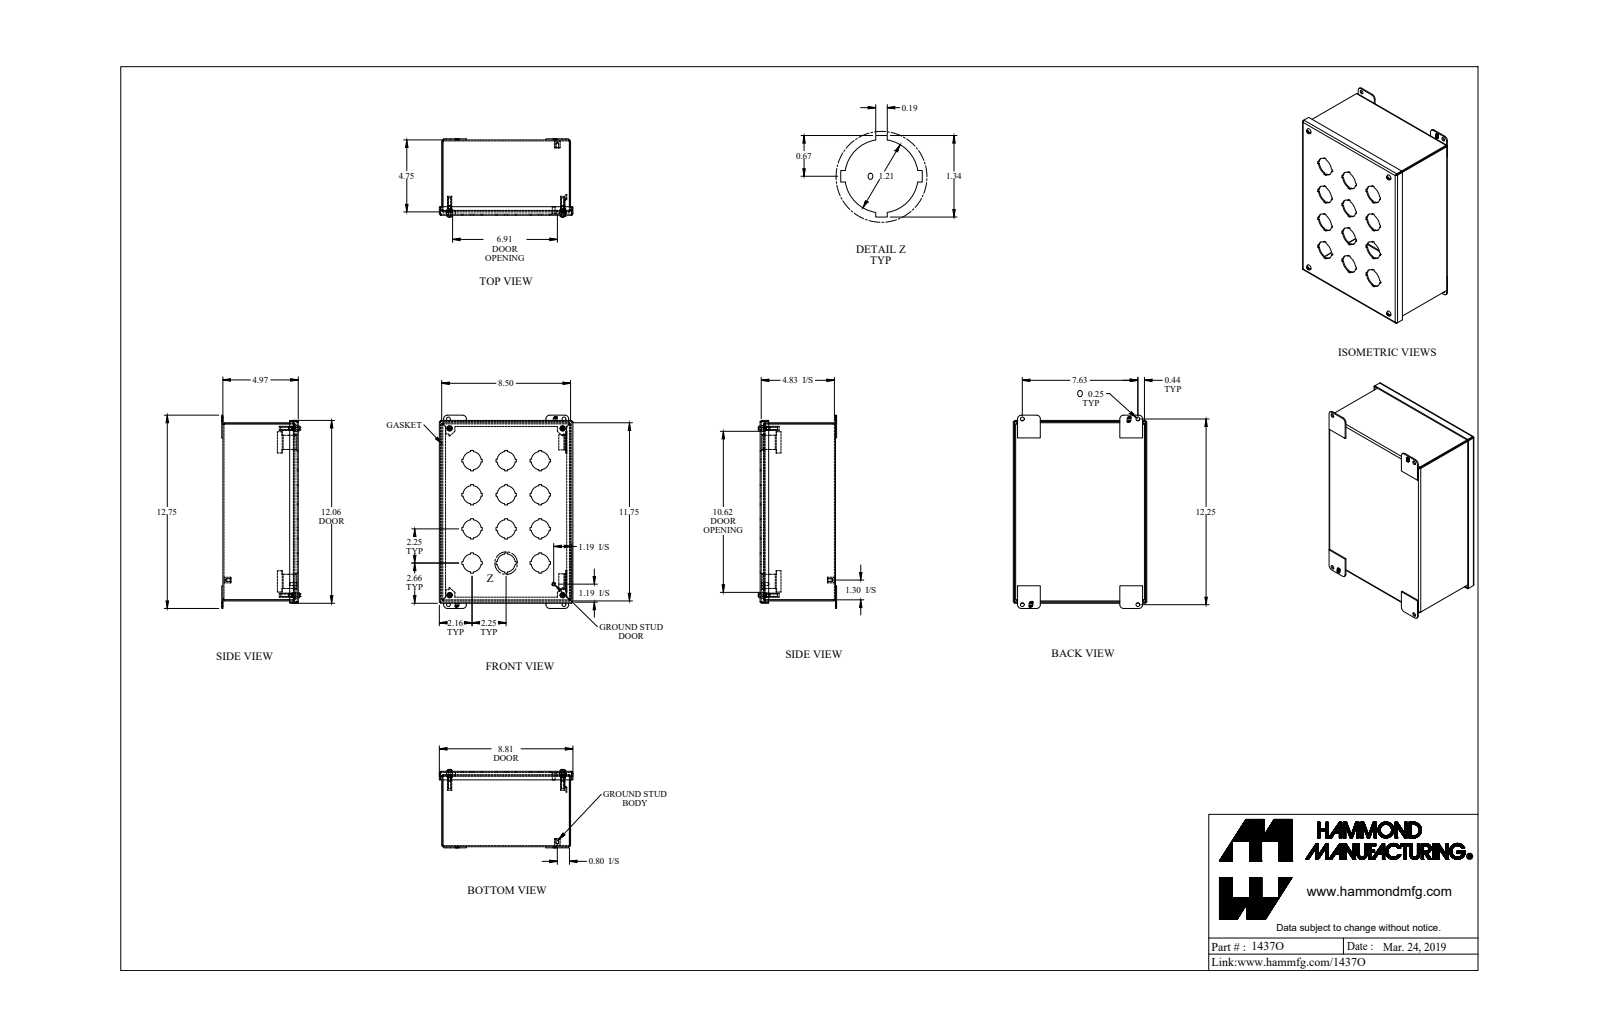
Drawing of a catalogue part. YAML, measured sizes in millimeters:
part_name: "1437O_Default"
step_written_by: "SolidWorks 2019 (CONFIG_CONTROL_DESIGN)"
units: millimeters
bodies: {solids: 23, faces: 907, planar: 643, cylindrical: 208, other: 56}
overall_size: [323.9, 223.8, 131.3]
volume: 557000
surface_area: 586600
round_holes:
  - {diameter: 30.7, count: 12}
  - {diameter: 6.4, count: 8}
  - {diameter: 4, count: 4}
  - {diameter: 10.3, count: 4}
  - {diameter: 4, count: 1}
round_bosses_or_shafts:
  - {diameter: 9.9, count: 4}
  - {diameter: 7, count: 4}
  - {diameter: 4.8, count: 4}
  - {diameter: 3.8, count: 4}
  - {diameter: 9.5, count: 1}
  - {diameter: 6.4, count: 1}
  - {diameter: 4.8, count: 1}
partial_cylinders:
  - {radius: 0.9, count: 12}
  - {radius: 2.7, count: 12}
  - {radius: 6.4, count: 8}
  - {radius: 0.7, count: 4}
  - {radius: 2.2, count: 4}
  - {radius: 4.1, count: 4}
  - {radius: 4.3, count: 4}
face_to_face_distances: [1.8, 124.5, 214.1, 126.3, 122.6, 1.8, 296.6, 212.2, 215.9, 298.5]
hole_center_spacings: [57.2, 127.8, 80.8, 114.3, 279.4, 295.3, 117.3, 16]
